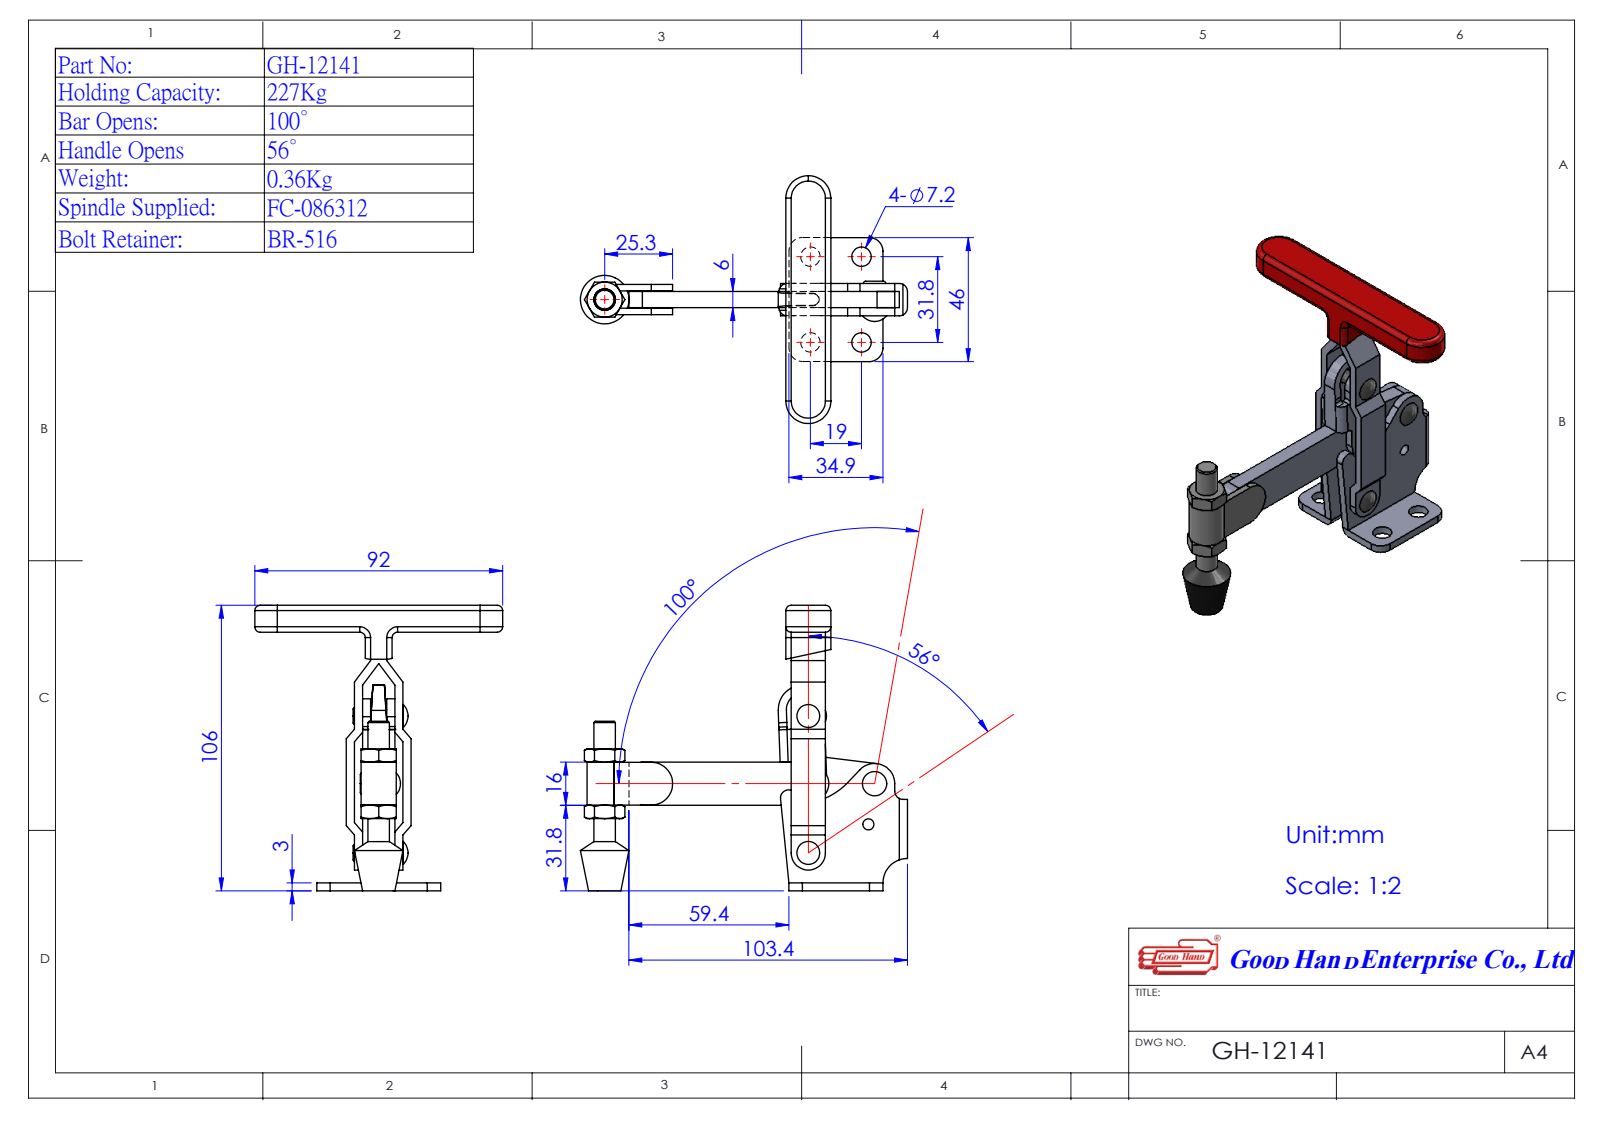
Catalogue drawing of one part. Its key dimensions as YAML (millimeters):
part_name: "Group2^GH-12141(簡化); GH-12141(簡化); Group5^GH-12141(簡化); 11214008-1^GH-12141(簡化) (+2 more)"
step_written_by: "SolidWorks 2016 (AUTOMOTIVE_DESIGN)"
units: millimeters
bodies: {solids: 5, faces: 263, planar: 126, cylindrical: 90, other: 47}
overall_size: [121.41, 106, 92]
volume: 58558
surface_area: 34092
round_holes:
  - {diameter: 4, count: 4}
  - {diameter: 7.2, count: 4}
round_bosses_or_shafts:
  - {diameter: 7.93, count: 1}
partial_cylinders:
  - {radius: 5, count: 6}
  - {radius: 3, count: 4}
  - {radius: 7.5, count: 4}
  - {radius: 1, count: 2}
  - {radius: 2.42, count: 2}
  - {radius: 6.4, count: 2}
  - {radius: 8.35, count: 2}
  - {radius: 9, count: 2}
face_to_face_distances: [3, 6, 9, 12, 15, 18, 10, 106, 96, 8.8]
hole_center_spacings: [19, 31.8, 37.04, 23.4, 25.13, 25.73, 35.14, 35.58]
